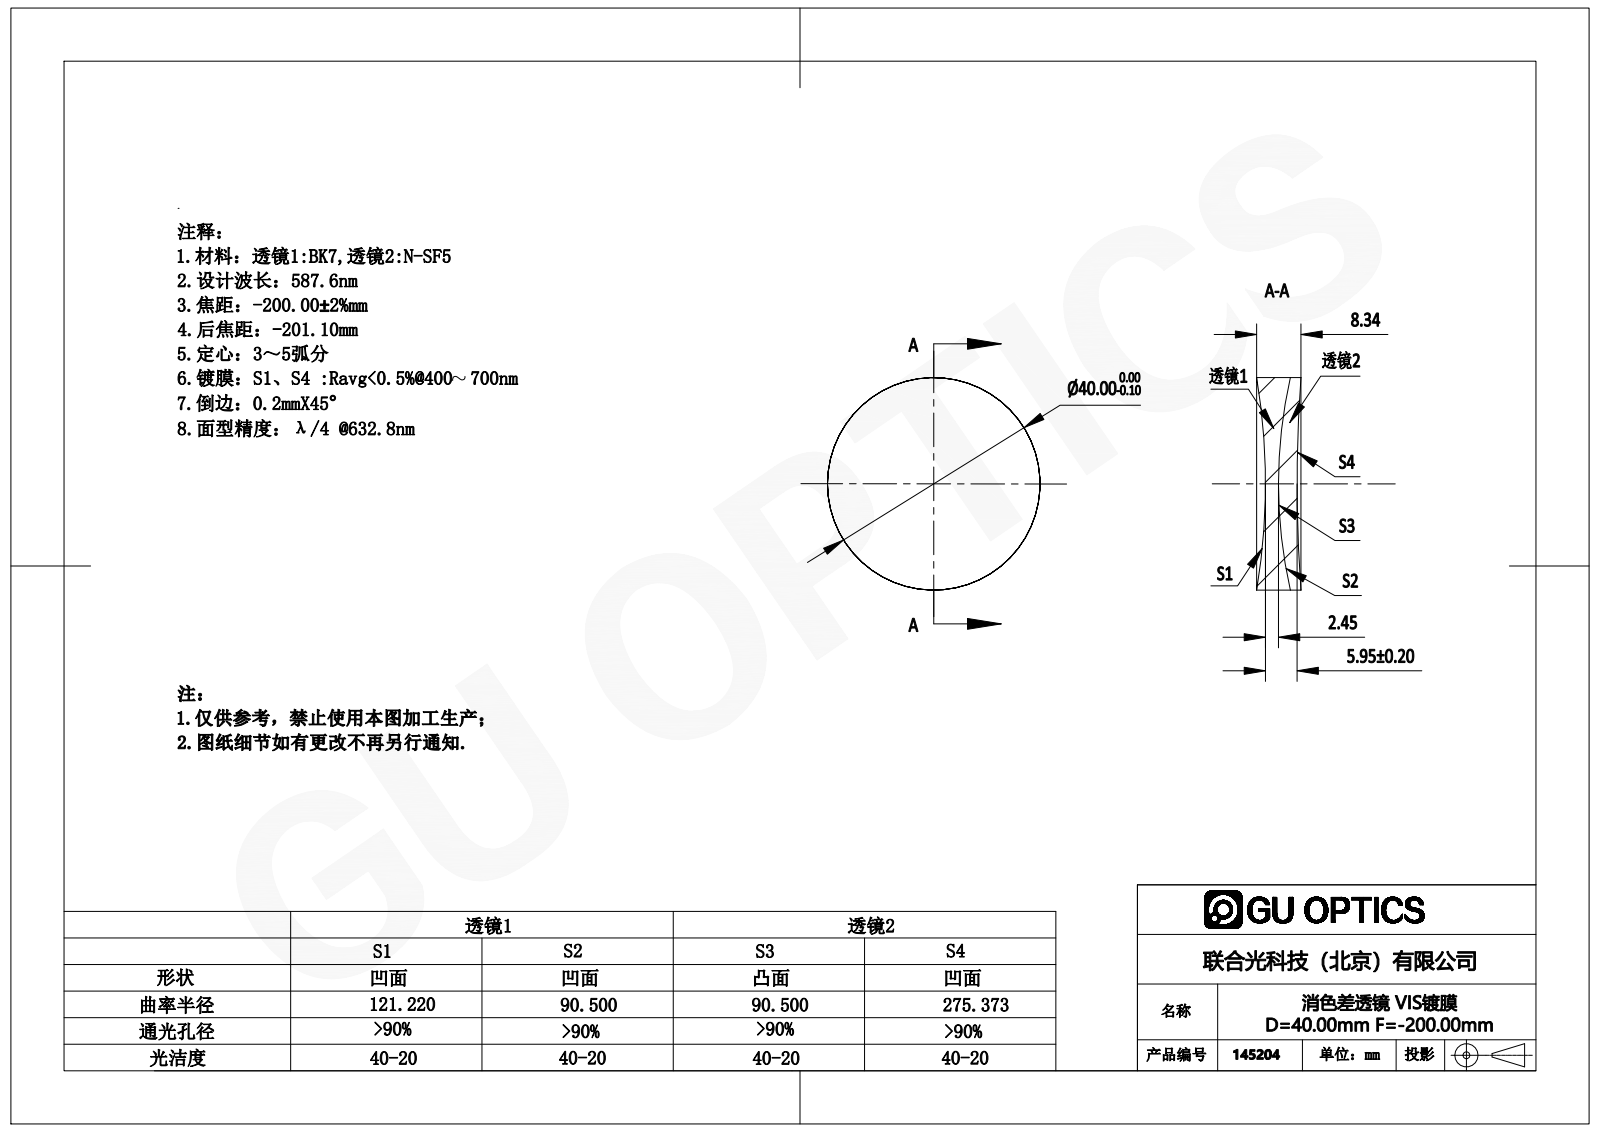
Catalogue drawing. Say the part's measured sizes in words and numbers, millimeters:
The part is named "145204". Its 3-D file was written by "SolidWorks 2016 (AUTOMOTIVE_DESIGN)". It is 2 solids with 12 faces: 0 planar, 4 cylindrical and 8 other. Overall it measures 40 by 40 by 8.34 millimeters. Its volume is 8 975 cubic millimeters and its surface area 6 116 square millimeters. Round bosses or shafts: 1 of diameter 40.
